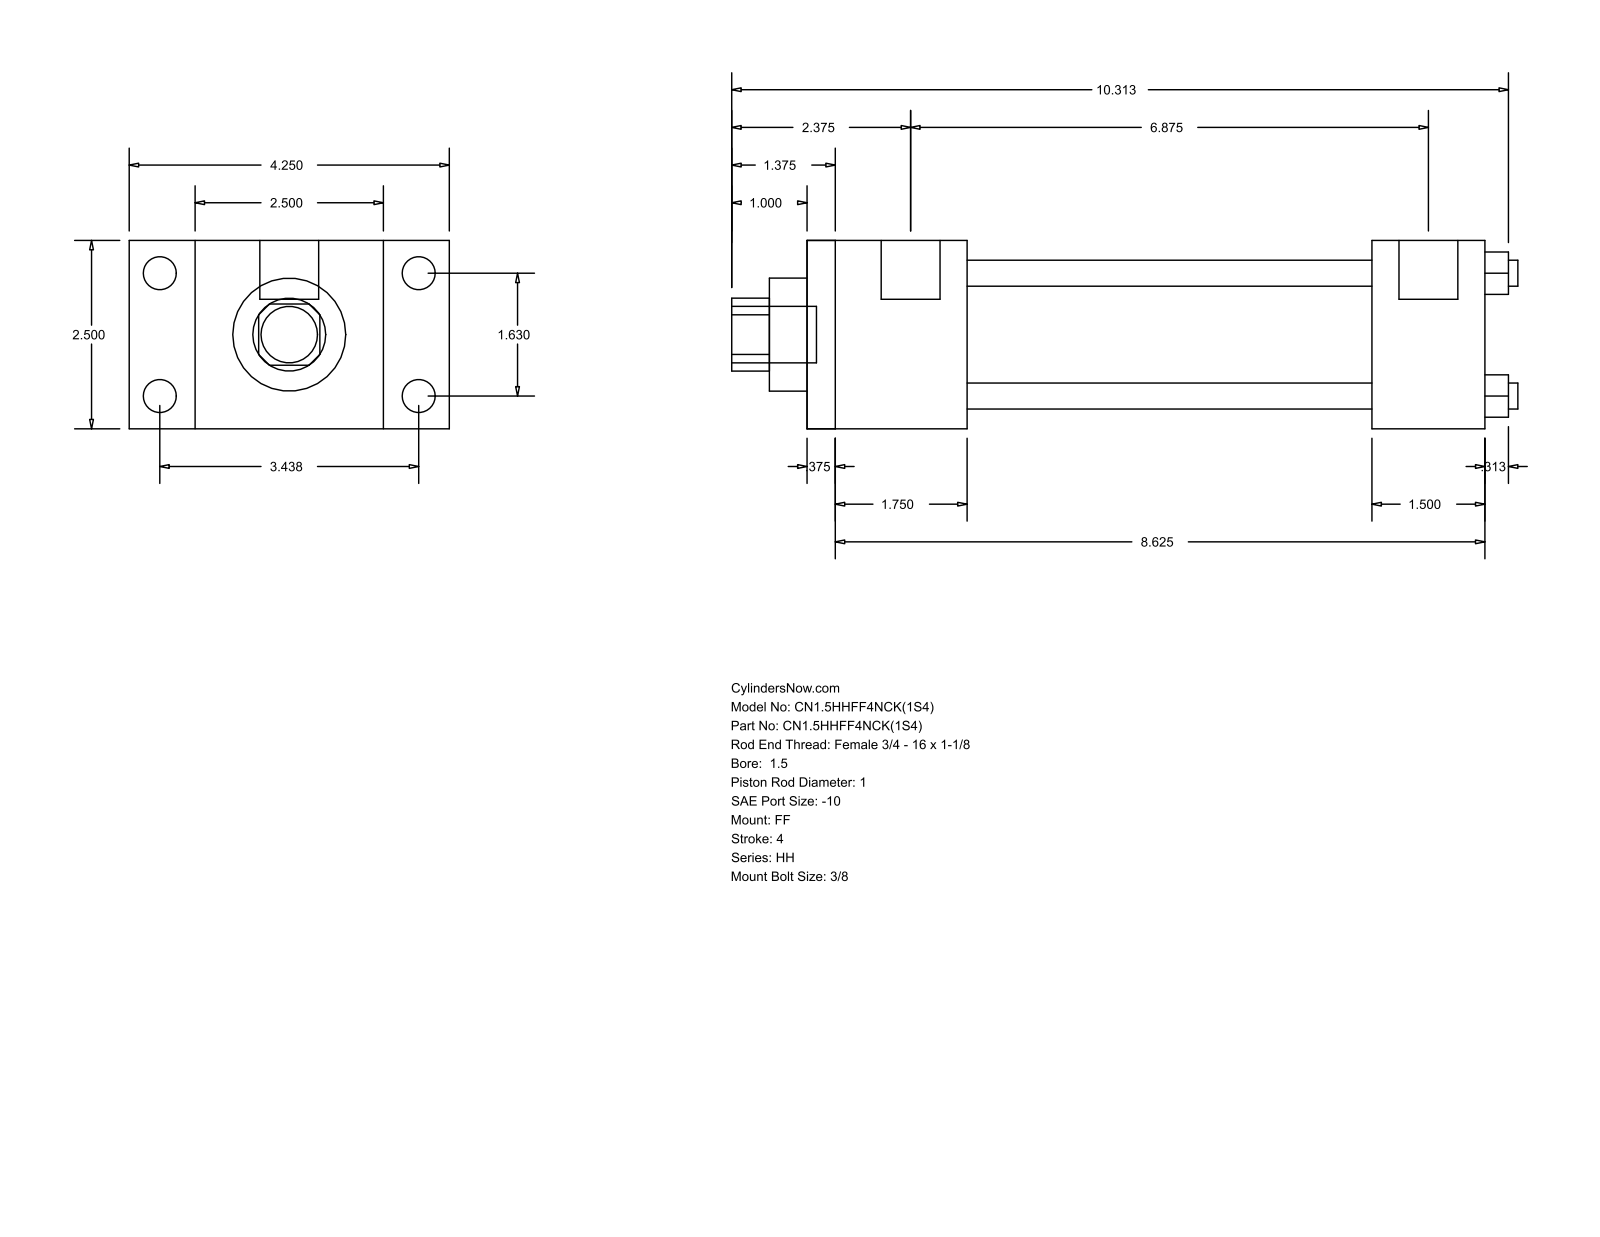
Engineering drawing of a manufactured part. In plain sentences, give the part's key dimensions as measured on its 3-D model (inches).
The part is named "HH_FF__0150_1". Its 3-D file was written by "GSSL Pune (CONFIG_CONTROL_DESIGN)". It is 0 solids with 92 faces: 64 planar, 28 cylindrical and 0 other. Overall it measures 10.437 by 4.25 by 2.5 inches. Round holes: 4 of diameter 0.345, 1 of diameter 1, 1 of diameter 1.5, 1 of diameter 1.75. Round bosses or shafts: 4 of diameter 0.438, 4 of diameter 0.219, 2 of diameter 0.781, 1 of diameter 0.75. Partial cylindrical surfaces (rounded edges, fillets, slot ends): 1 of radius 0.484. The main face-to-face distances are 2.5, 9, 0.375, 8.625, 2.125, 1.75, 6.875, 7.5, 7.125, 5.375. The hole center spacings are 1.152, 1.63, 2.305.
